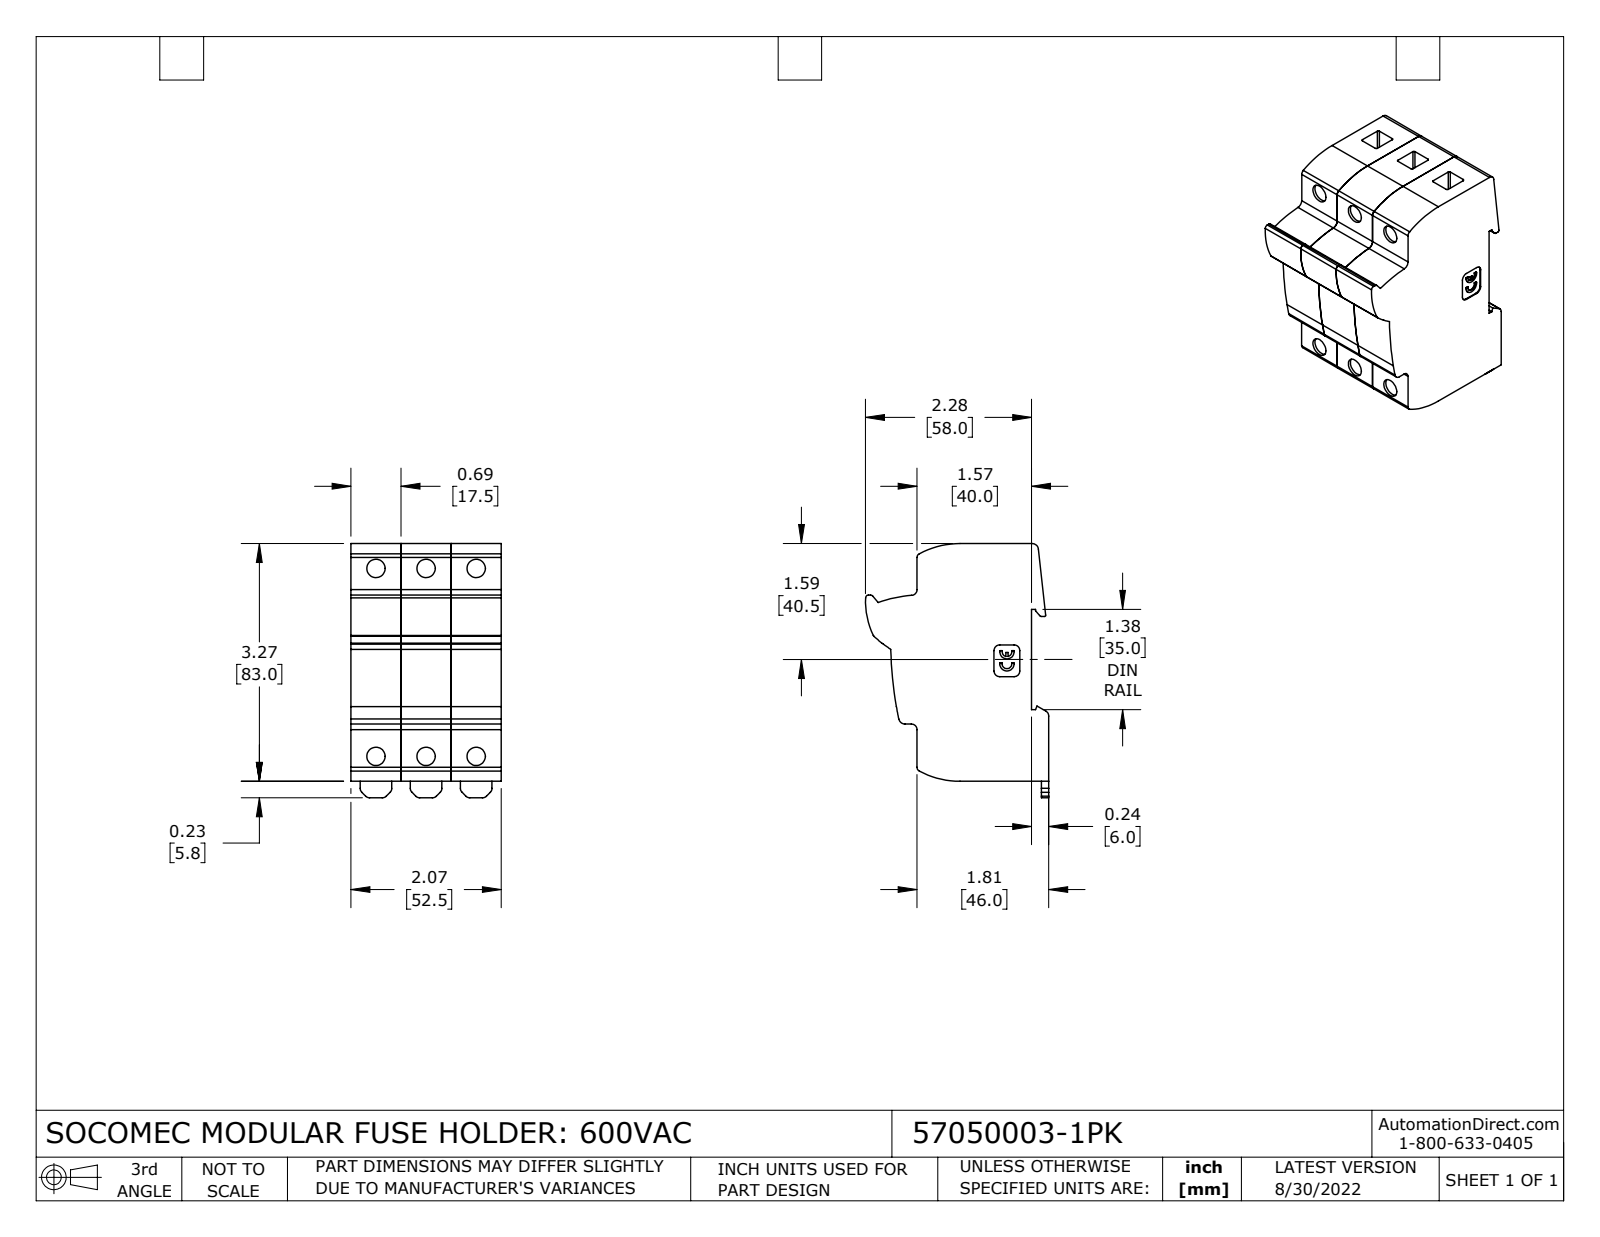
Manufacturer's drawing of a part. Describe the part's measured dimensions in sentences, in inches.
The part is named "57050003-1PK". Its 3-D file was written by "SolidWorks 2021 (CONFIG_CONTROL_DESIGN)". It is 3 solids with 315 faces: 156 planar, 159 cylindrical and 0 other. Overall it measures 3.496 by 2.52 by 2.067 inches. Its volume is 12.69 cubic inches and its surface area 64 square inches. Round holes: 6 of diameter 0.252. Partial cylindrical surfaces (rounded edges, fillets, slot ends): 19 of radius 0.079, 13 of radius 0.02, 4 of radius 0.039, 2 of radius 0.059, 2 of radius 0.067, 2 of radius 0.087, 2 of radius 0.098, 2 of radius 1.186. The main face-to-face distances are 0.689, 1.378, 2.067, 0.236, 1.575, 3.268, 1.811, 0.199, 0.49, 0.888. The hole center spacings are 0.689, 2.673, 2.583, 1.378, 2.927.
